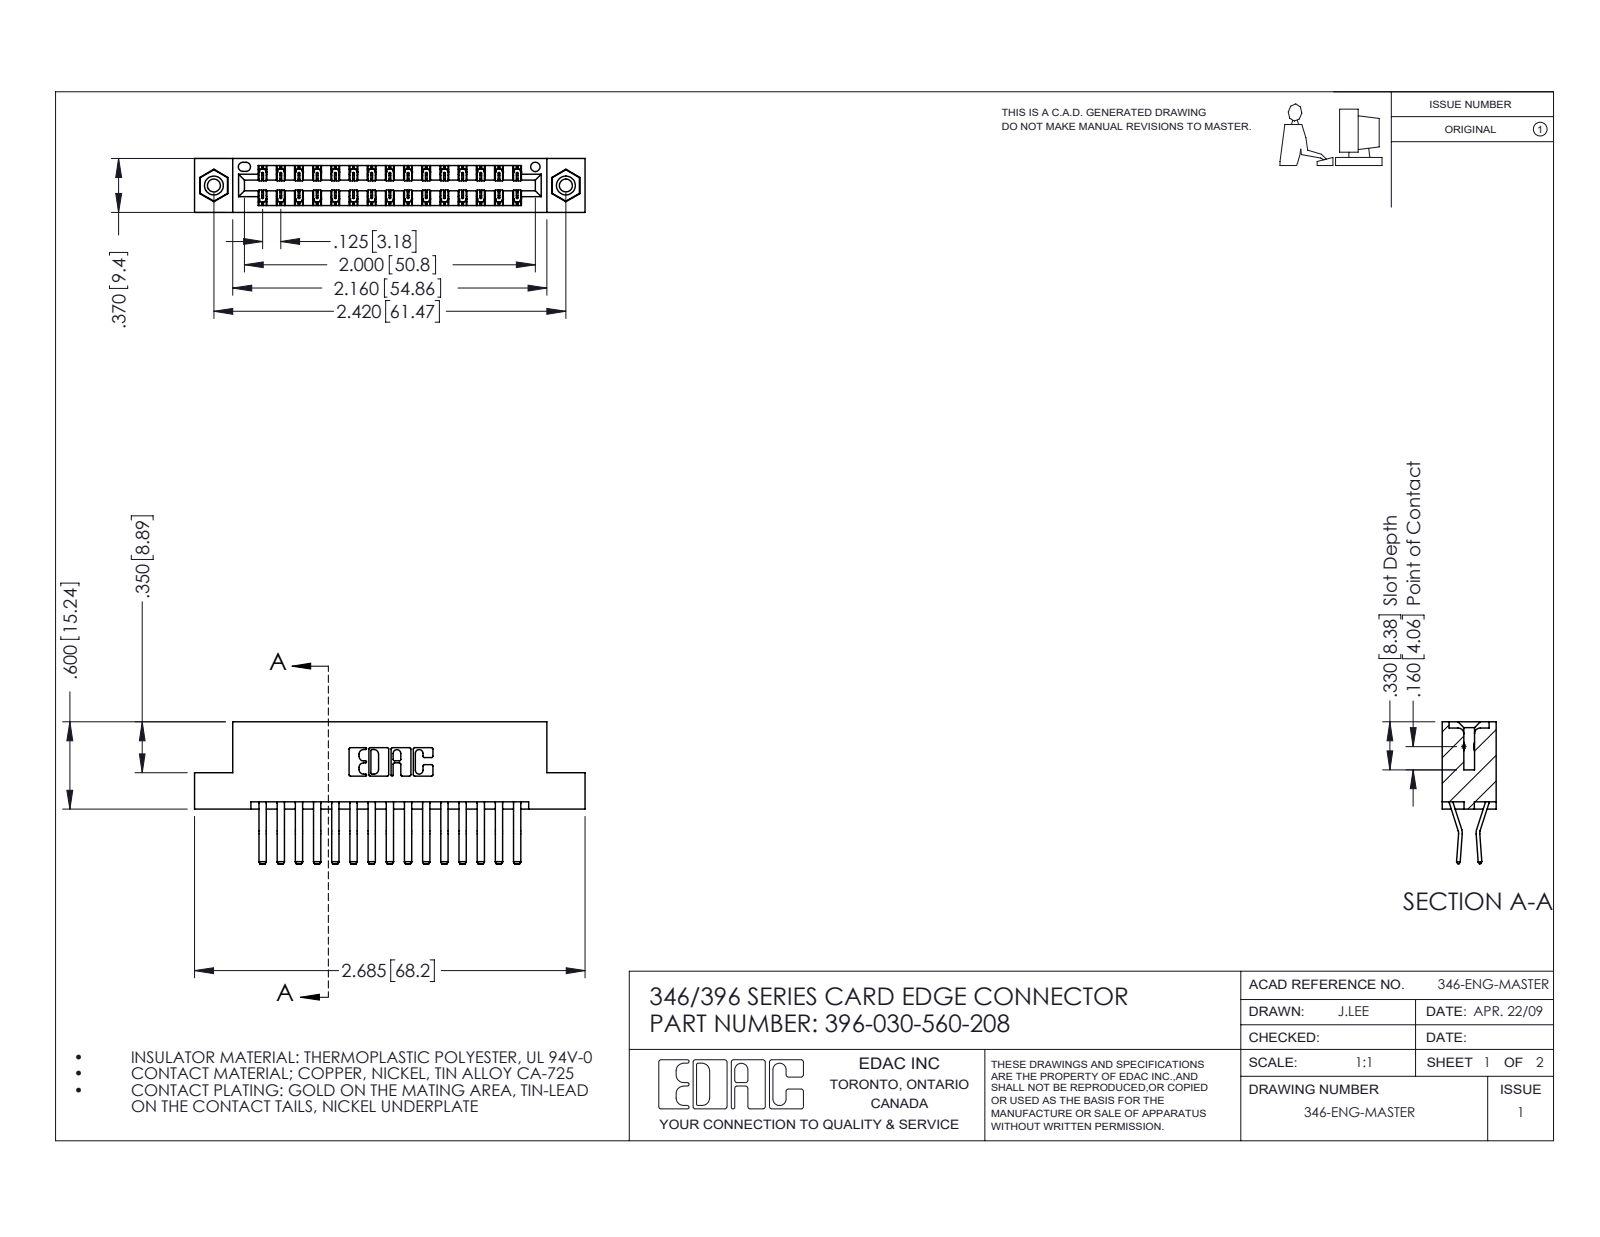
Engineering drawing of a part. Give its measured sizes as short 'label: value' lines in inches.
name: 396-030-560-208; 346 Part_Flush Mounting Lugs - 0.156 Dia-TI; 345-292-001_560 Tail; 345-250-001_345-250-003-102
written by: SolidWorks 2016 (CONFIG_CONTROL_DESIGN)
unit: in
bodies: 33 solids, 1802 faces (1158 planar, 628 cylindrical, 16 other)
size: 2.685 × 0.975 × 0.37
volume: 0.405 in³; area: 14.31 in²
holes: 2× ⌀0.089, 2× ⌀0.125, 2× ⌀0.156, 1× ⌀0.064
bosses: 2× ⌀0.155
rounds: 45× R0.006, 22× R0.01, 6× R0.007, 6× R0.031, 3× R0.026, 2× R0.01, 2× R0.014, 2× R0.022
face distances: 0.048, 0.322, 0.25, 0.37, 0.025, 0.072, 0.298, 0.275, 0.148, 0.222
hole spacings: 0.246, 2.213, 2.42
